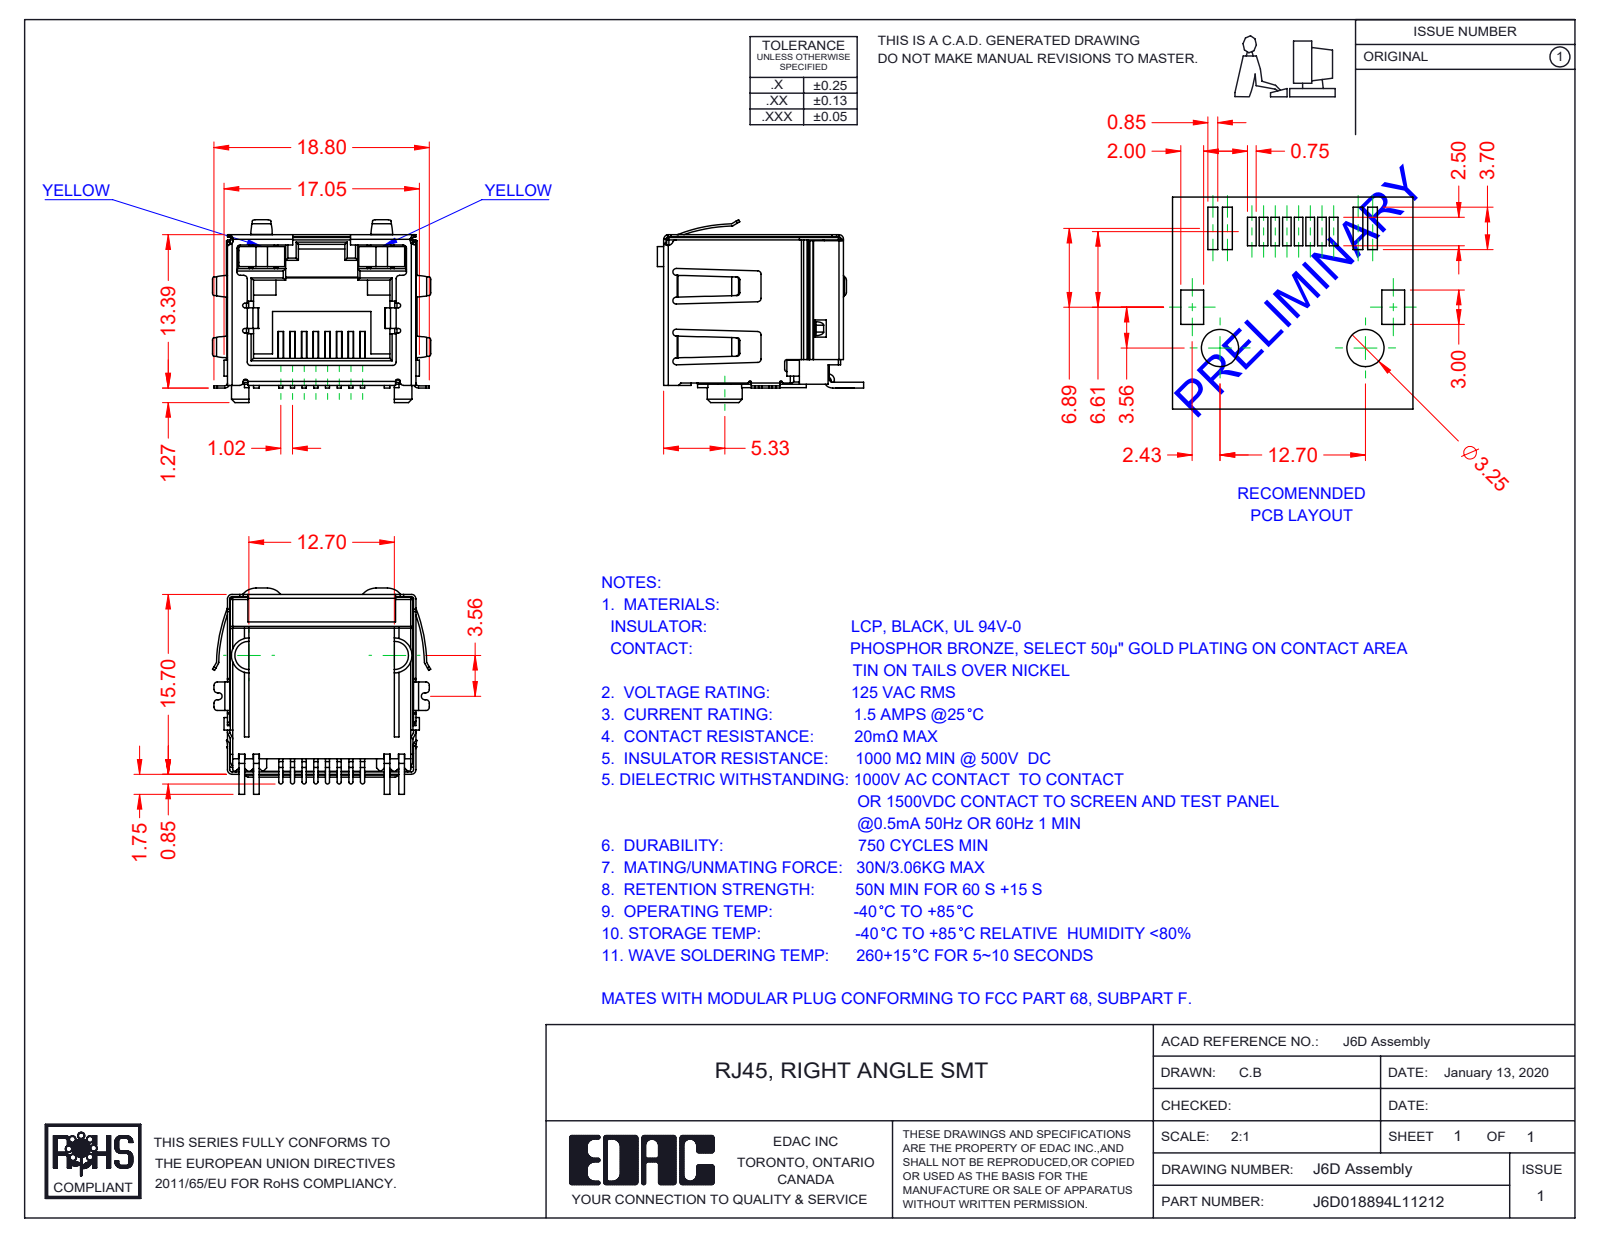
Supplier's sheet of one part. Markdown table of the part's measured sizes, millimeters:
| quantity | value |
| --- | --- |
| part name | 6D Contacts; 6D LED LH_1-Yellow; 6D Shield_LED - EMI; J6D018894L11212 (+2 more) |
| STEP written by | SolidWorks 2016 (CONFIG_CONTROL_DESIGN) |
| units | millimeters |
| bodies | 12 solids, 1028 faces (701 planar, 282 cylindrical, 45 other) |
| overall size | 19.06 × 18 × 15.95 |
| volume | 1 790 mm³ |
| surface area | 4 796 mm² |
| partial cylindrical surfaces (radius × count) | 0.3 × 55, 0.2 × 40, 0.4 × 19, 0.25 × 16, 0.1 × 12, 0.15 × 8, 0.18 × 8, 0.5 × 6 |
| main face-to-face distances | 16, 16.2, 16.25, 2.25, 1, 15.95, 12.8, 0.45, 13.05, 10.6 |
